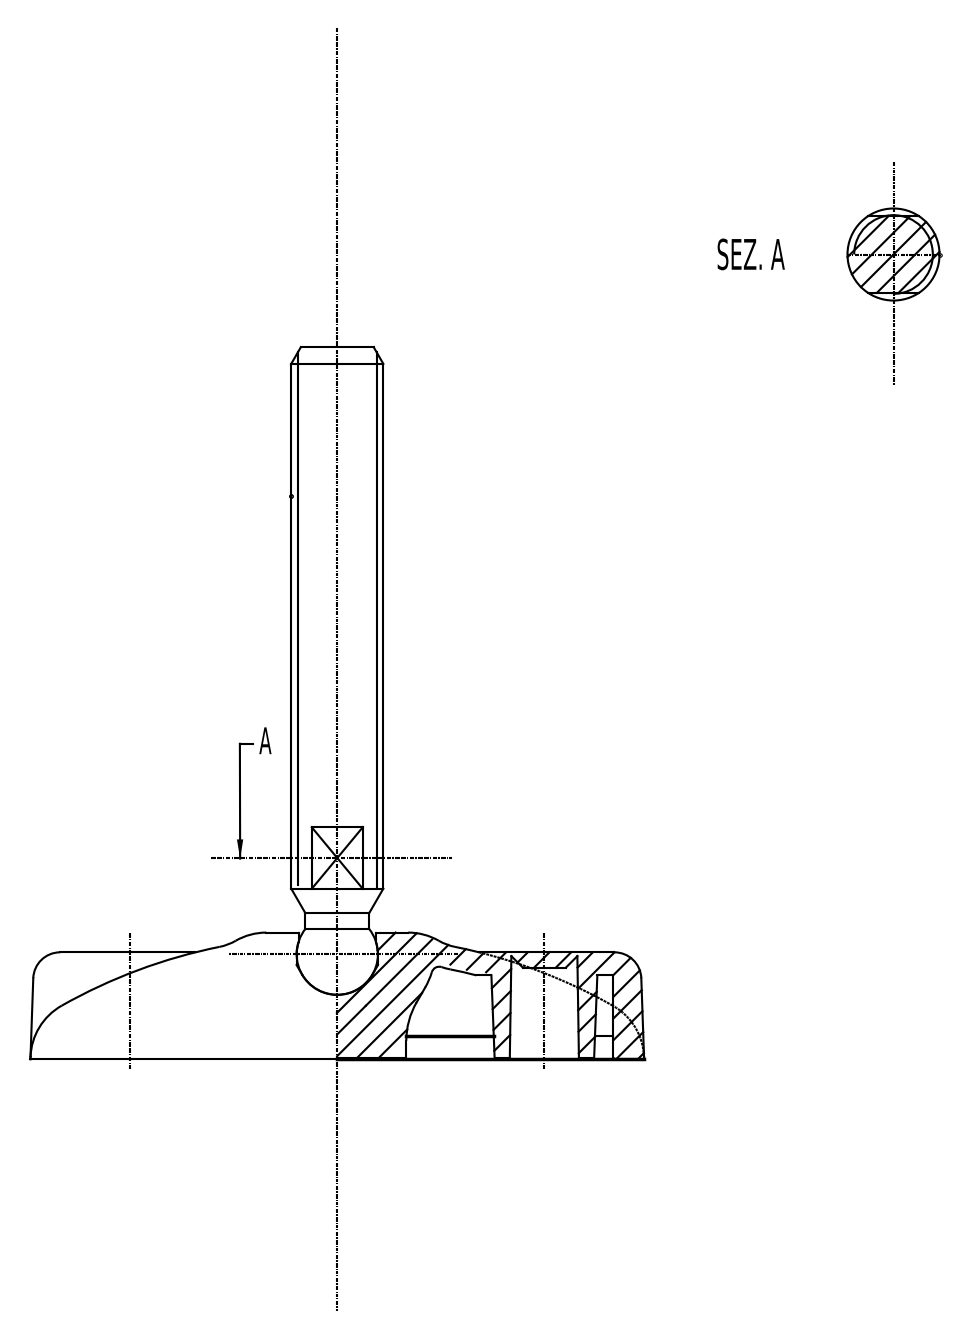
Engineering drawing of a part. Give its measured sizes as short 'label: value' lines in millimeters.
written by: THINKDESIGN (CONFIG_CONTROL_DESIGN)
unit: mm
bodies: 2 solids, 57 faces (10 planar, 5 cylindrical, 42 other)
size: 146.54 × 80.01 × 80.01
volume: 65 218 mm³; area: 18 201 mm²
bosses: 1× ⌀12, 1× ⌀7.7
rounds: 2× R0.5, 1× R9
face distances: 14.33, 11.33, 3, 16.5, 5.17, 2.17, 146.54, 135.21, 132.21, 130.04
